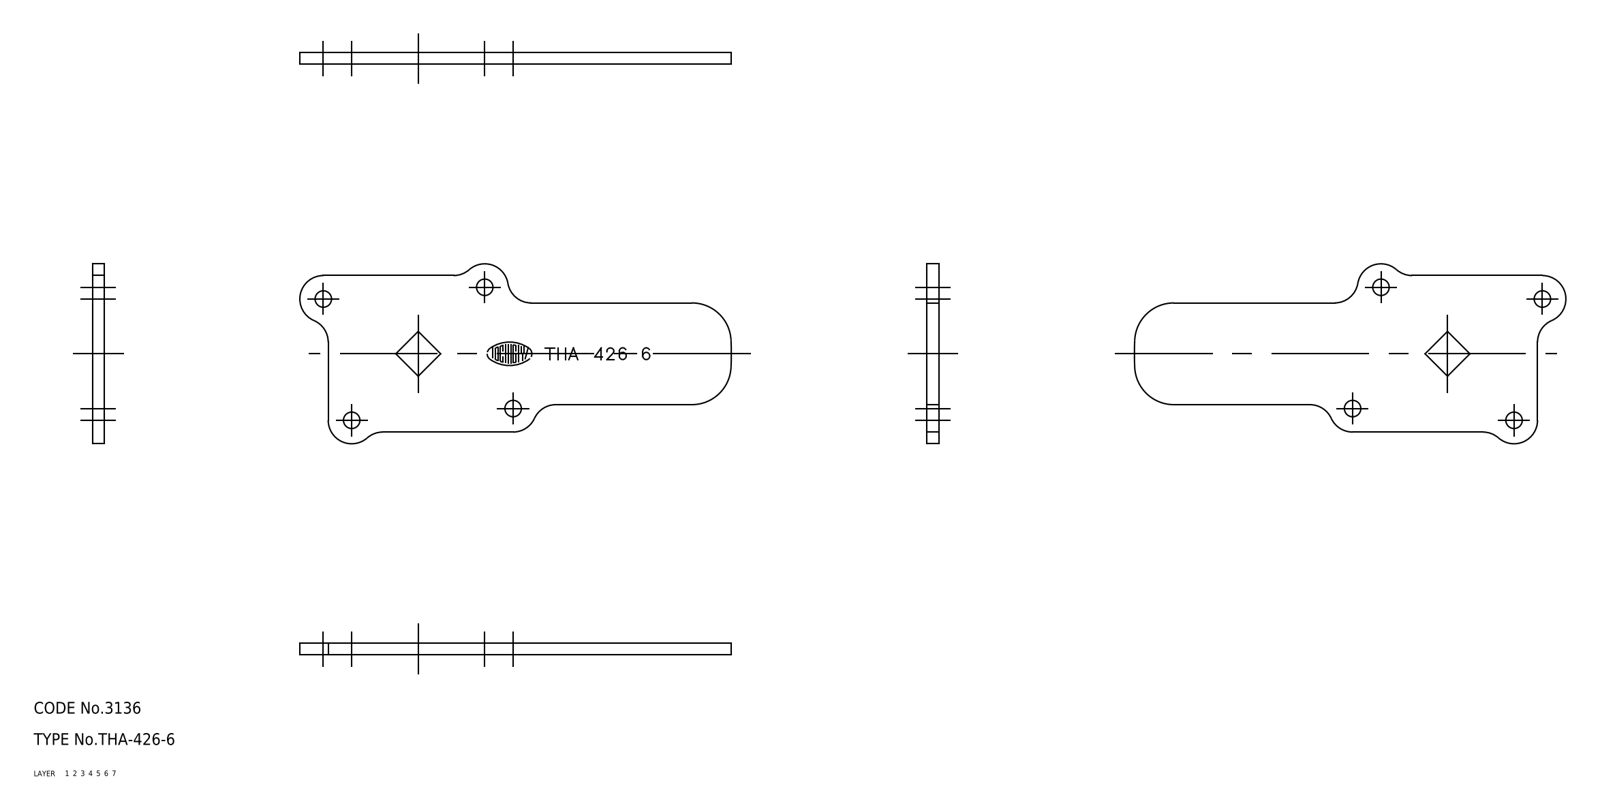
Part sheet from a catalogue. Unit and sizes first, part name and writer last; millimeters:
Units: millimetres
Overall size (bounding box): 110.25 × 46 × 3
Volume: 9 991 mm³ · Surface area: 7 759 mm²
Bodies: 1 solid, 31 faces (0 planar, 0 cylindrical, 31 other)
Part name (STEP PRODUCT): cam
STEP written by: CADfix (AUTOMOTIVE_DESIGN)
